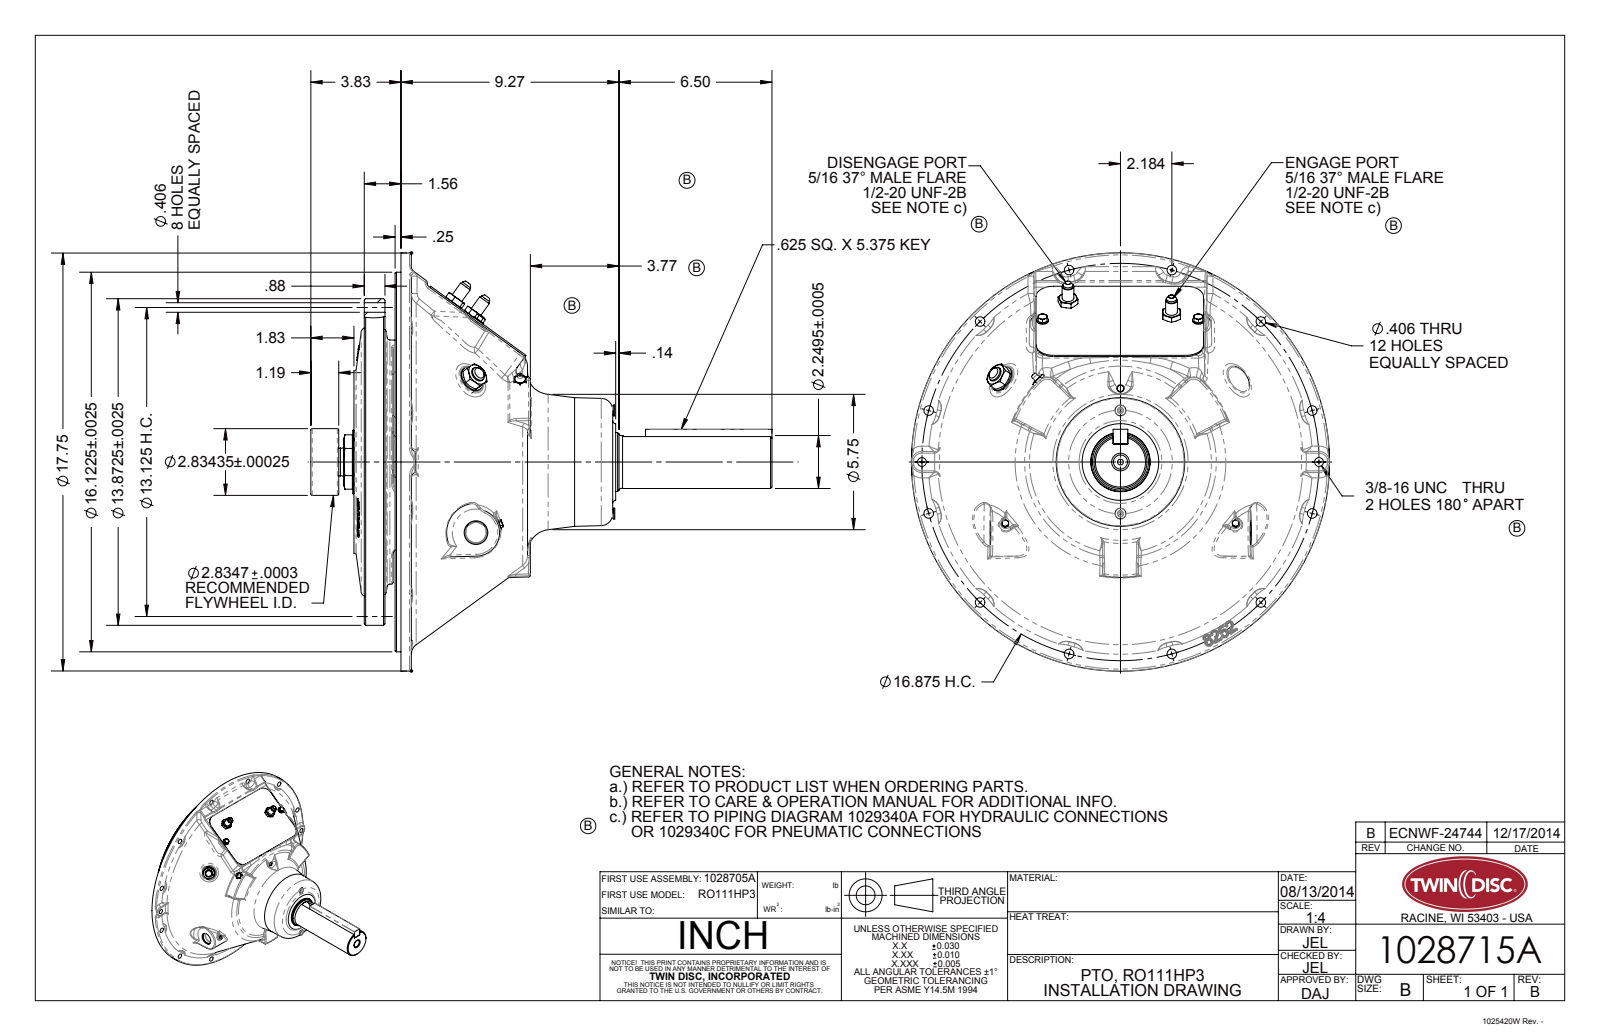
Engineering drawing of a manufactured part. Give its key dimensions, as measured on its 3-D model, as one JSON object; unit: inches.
{"part_name": "1028715A", "step_written_by": "SolidWorks 2010 (AUTOMOTIVE_DESIGN)", "units": "inches", "bodies": {"solids": 0, "faces": 1102, "planar": 248, "cylindrical": 205, "other": 649}, "overall_size": [19.597, 17.773, 17.773], "round_holes": [[0.406, 20], [0.234, 2], [0.375, 2], [0.375, 2], [0.422, 2], [0.875, 2], [0.313, 1], [1.006, 1], [1.181, 1], [1.936, 1], [2.428, 1], [11.787, 1]], "round_bosses_or_shafts": [[0.5, 4], [0.46, 2], [0.426, 2], [16.122, 1], [13.872, 1], [11.375, 1], [2.834, 1], [2.7, 1]], "partial_cylinders_radius": [[0.08, 24], [0.02, 13], [0.25, 10], [0.13, 6], [0.75, 4], [2.052, 4], [0.01, 2], [0.06, 2]], "face_to_face_distances": [1.387, 1.56, 0.173, 0.064, 2, 0.44, 1.827, 2.439, 1.998, 0.612], "hole_center_spacings": [8.437, 11.932, 14.614, 16.3, 2.7, 4.284, 4.367, 5.023]}
